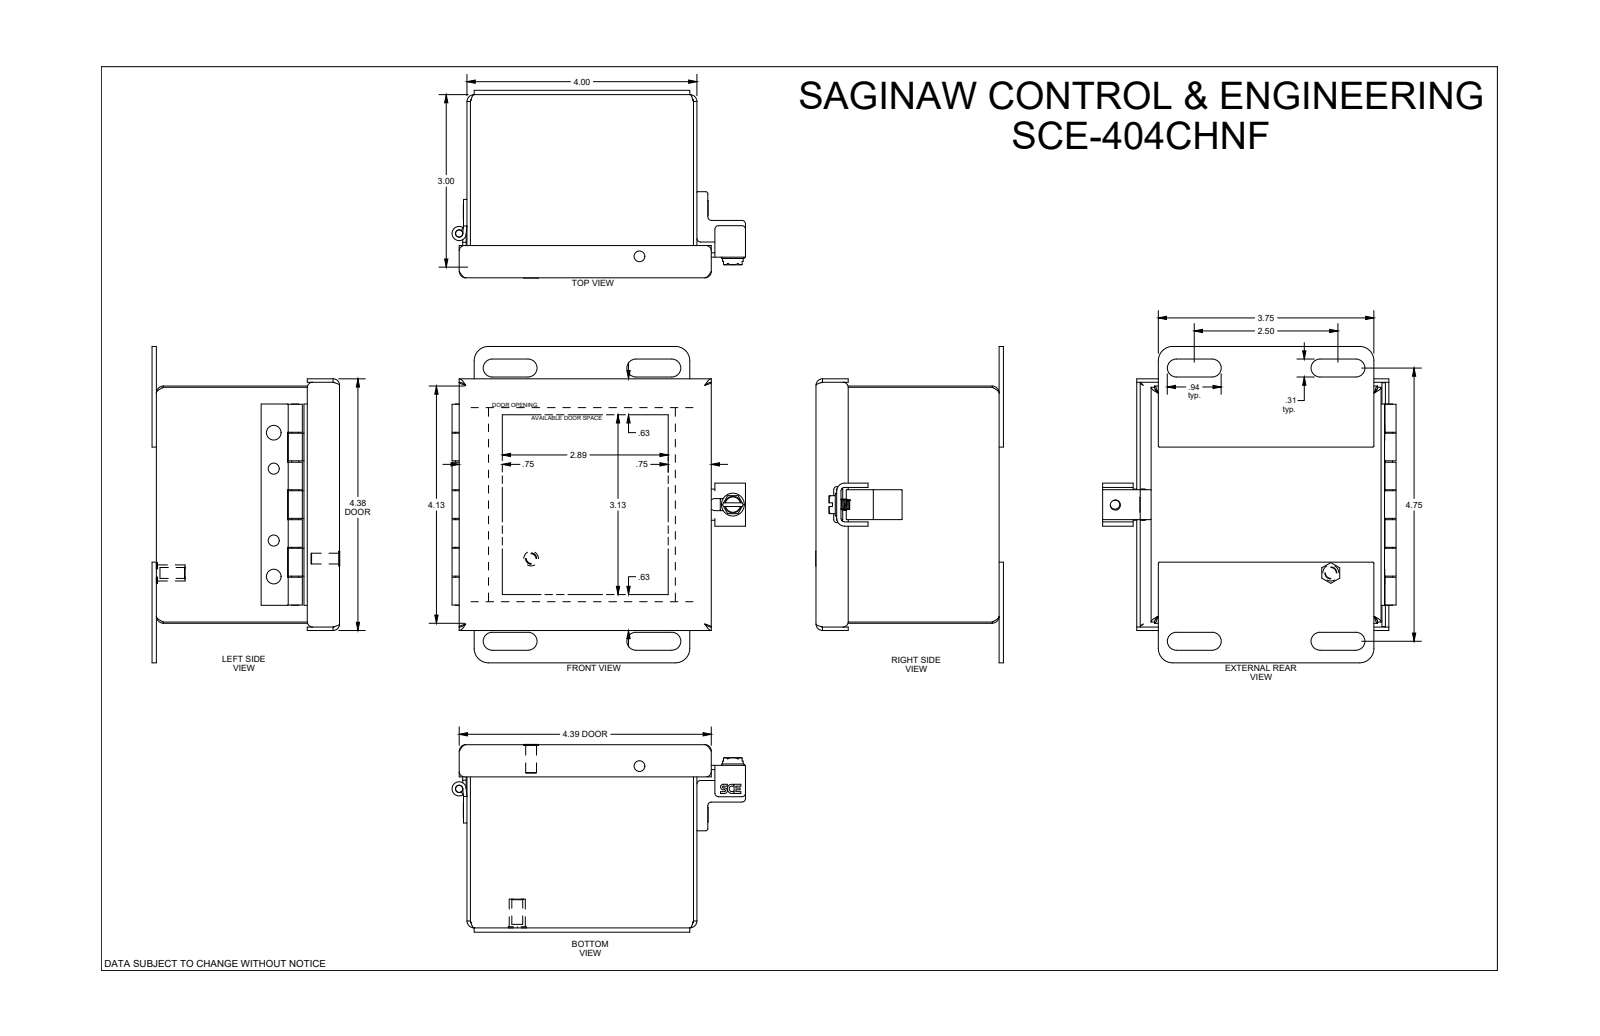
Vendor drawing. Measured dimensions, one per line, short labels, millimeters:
name: SCE-404CHNF
written by: SolidWorks 2019 (CONFIG_CONTROL_DESIGN)
unit: mm
bodies: 0 solids, 687 faces (316 planar, 207 cylindrical, 164 other)
size: 139.7 × 129.6 × 82.9
holes: 5× ⌀4.9, 4× ⌀4.8, 1× ⌀3.2, 1× ⌀4, 1× ⌀4.7, 1× ⌀4.9, 1× ⌀6.8, 1× ⌀7.1
bosses: 5× ⌀4.8, 4× ⌀6.5, 1× ⌀10.1, 1× ⌀7.1, 1× ⌀6.2, 1× ⌀3.1
rounds: 50× R0.3, 13× R1.5, 8× R1.3, 8× R2.8, 8× R4, 5× R2.3, 4× R0.1, 4× R0.5
face distances: 1.5, 79.4, 100.1, 103.3, 80.9, 77.9, 1.9, 3.4, 101.6, 81.3
hole spacings: 31.8, 8.8, 15.9, 15.9, 16, 16, 31.8, 47.6
